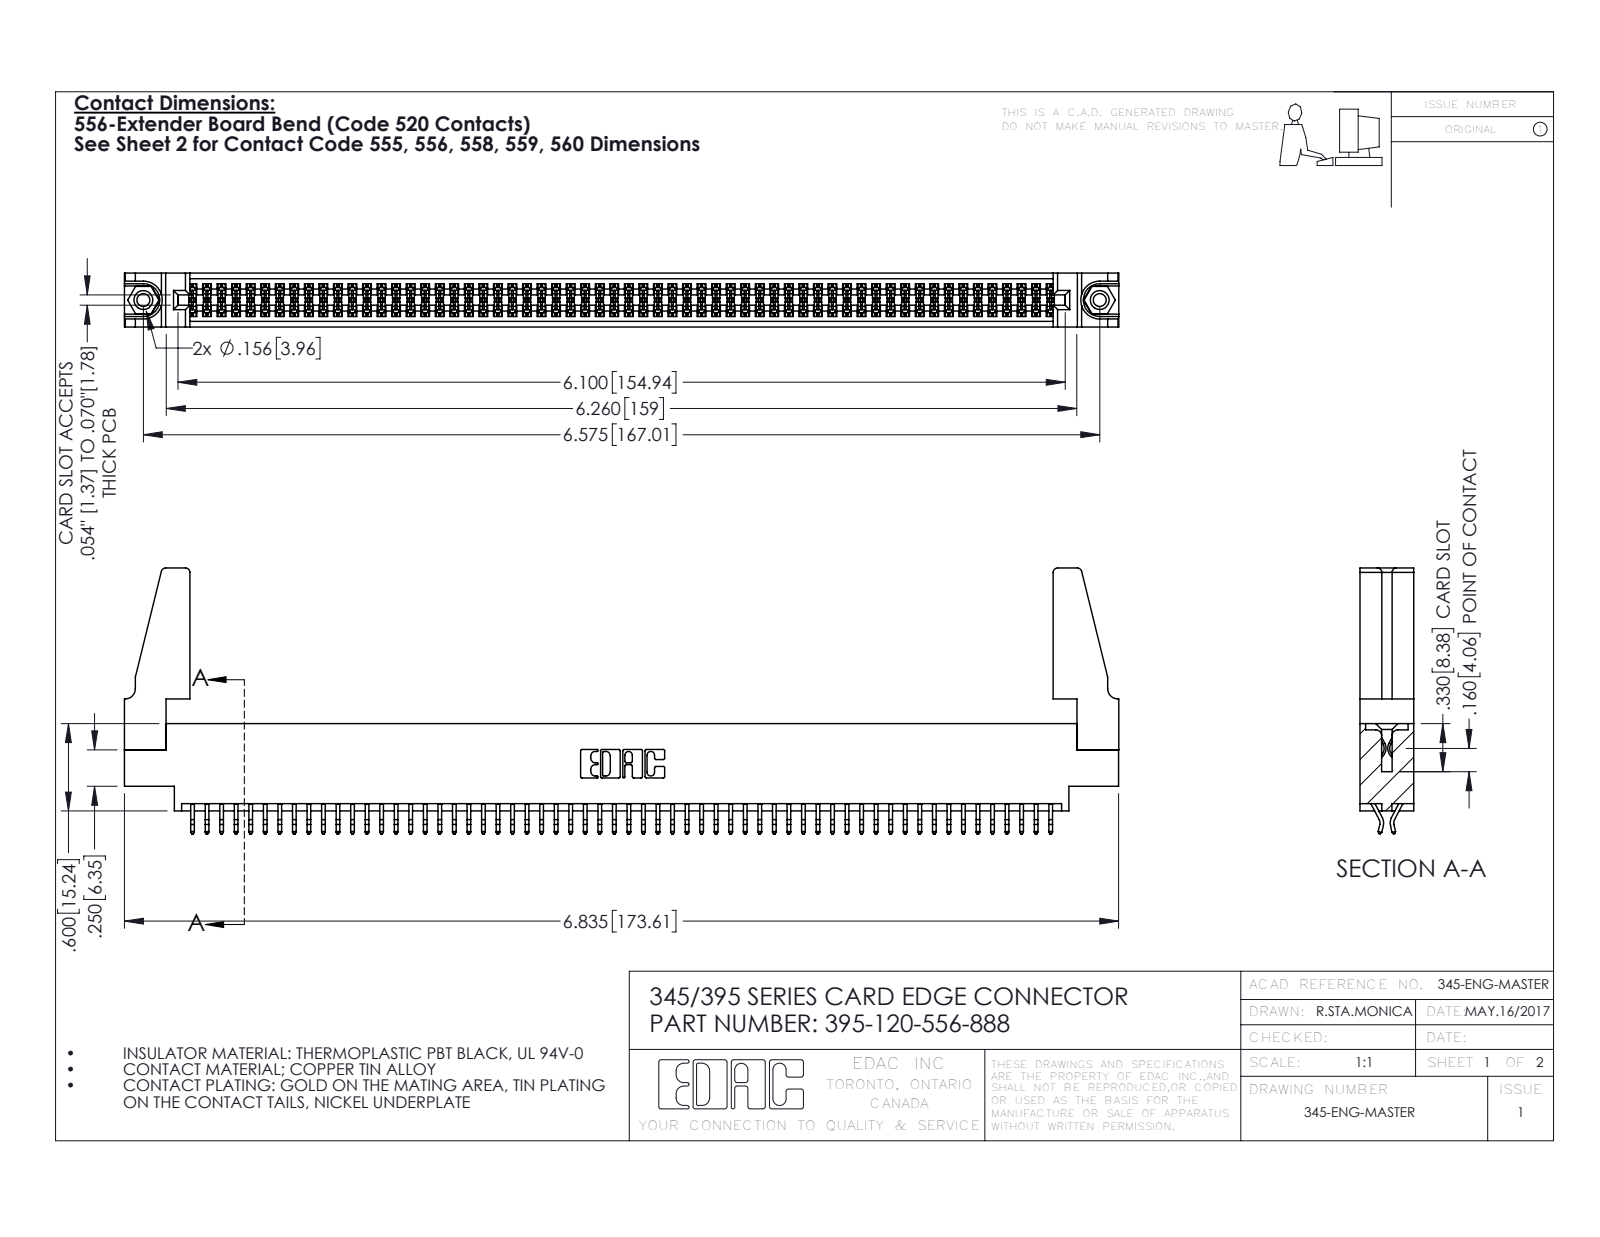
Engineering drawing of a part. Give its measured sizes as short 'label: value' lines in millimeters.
name: 345-220-078_345-220-088; 345 Part_0.170 Offset - 0.156 Dia-TH; 345-292-001_556 Tail; 345-250-001_345-250-001-102 (+1 more)
written by: SolidWorks 2016 (CONFIG_CONTROL_DESIGN)
unit: mm
bodies: 125 solids, 6974 faces (4596 planar, 2362 cylindrical, 16 other)
size: 173.6 × 46.4 × 9.4
volume: 20 170 mm³; area: 28 520 mm²
holes: 2× ⌀2.3, 2× ⌀3.2, 2× ⌀4, 1× ⌀1.6
bosses: 2× ⌀3.9
rounds: 180× R0.2, 22× R0.3, 8× R0.8, 6× R0.2, 6× R0.8, 3× R0.7, 2× R0.3, 2× R0.4
face distances: 1.8, 7.6, 9.4, 0.6, 2.5, 6.9, 5.1, 5.7, 4.4, 3.8
hole spacings: 6.9, 161, 167
